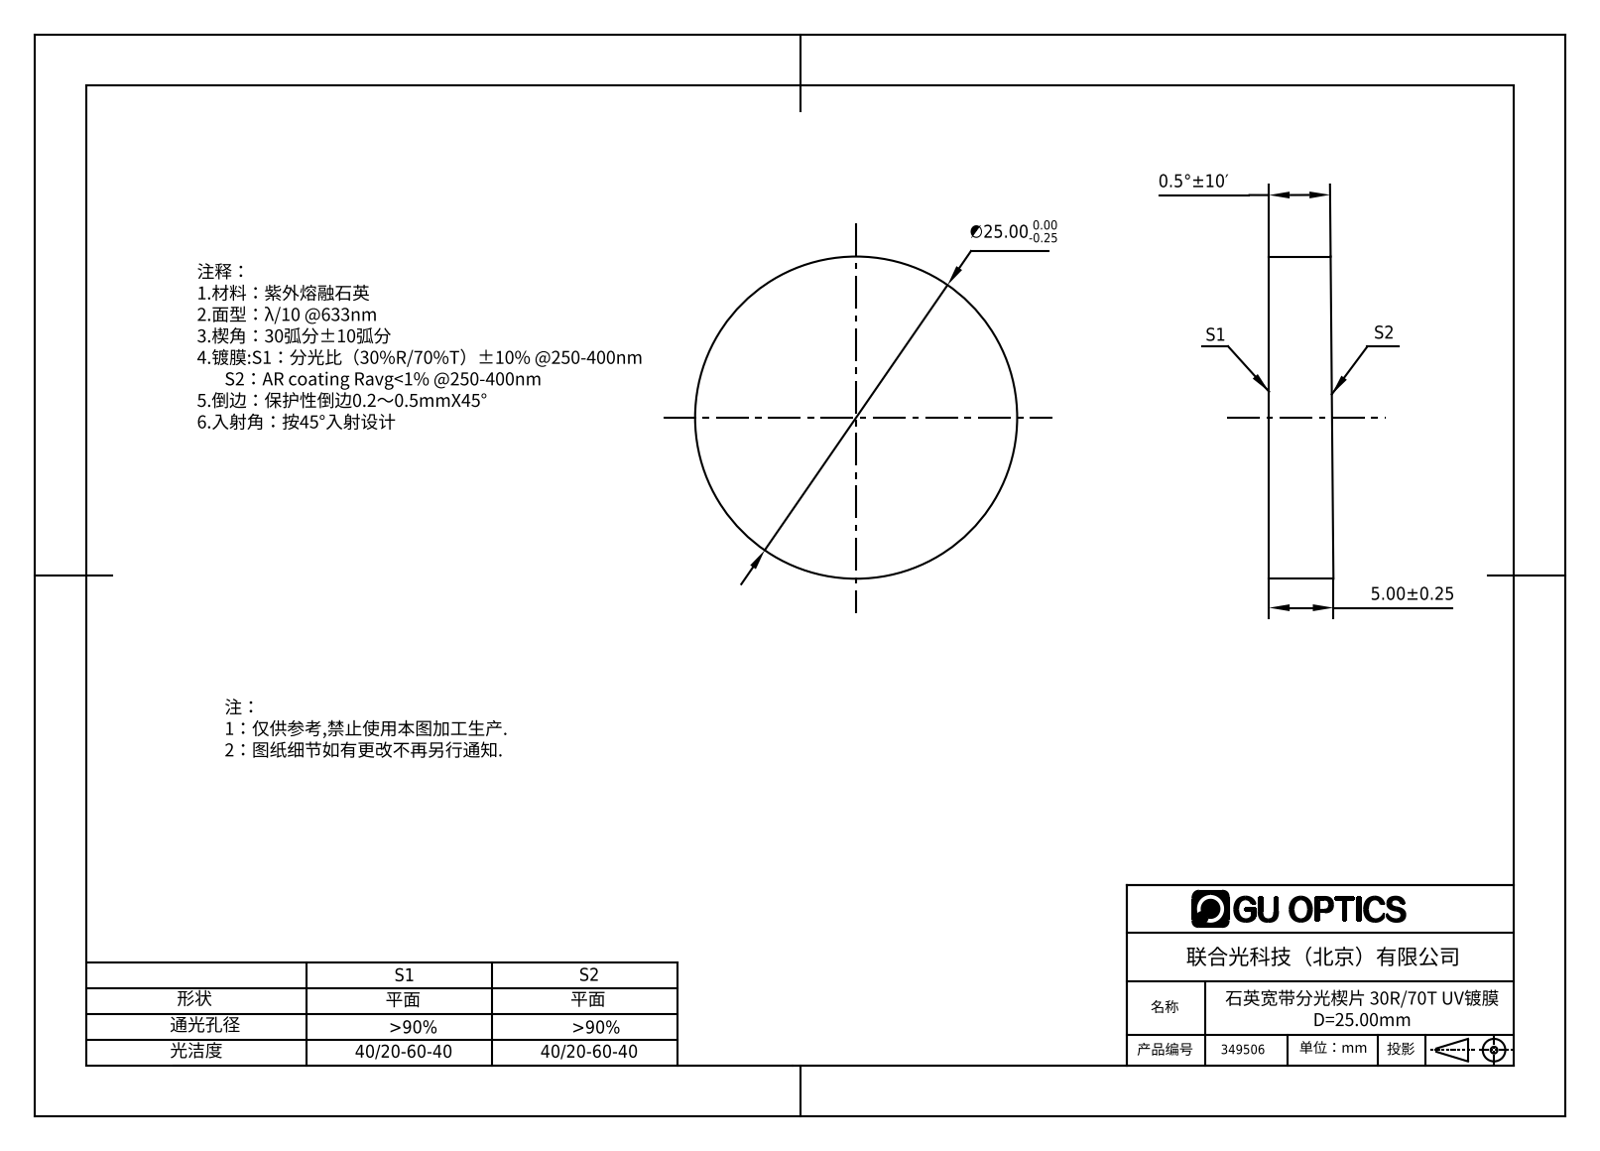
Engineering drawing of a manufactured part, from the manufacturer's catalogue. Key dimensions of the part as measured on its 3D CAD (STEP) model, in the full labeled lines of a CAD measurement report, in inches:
Part name (STEP PRODUCT): 349506
STEP written by: SolidWorks 2016 (AUTOMOTIVE_DESIGN)
Units: inches
Bodies: 1 solid, 4 faces (2 planar, 2 cylindrical, 0 other)
Overall size (bounding box): 0.984 × 0.984 × 0.197
Volume: 0.147 in³ · Surface area: 2.117 in²
Round bosses / shafts (diameter × count): ⌀0.984 ×1
